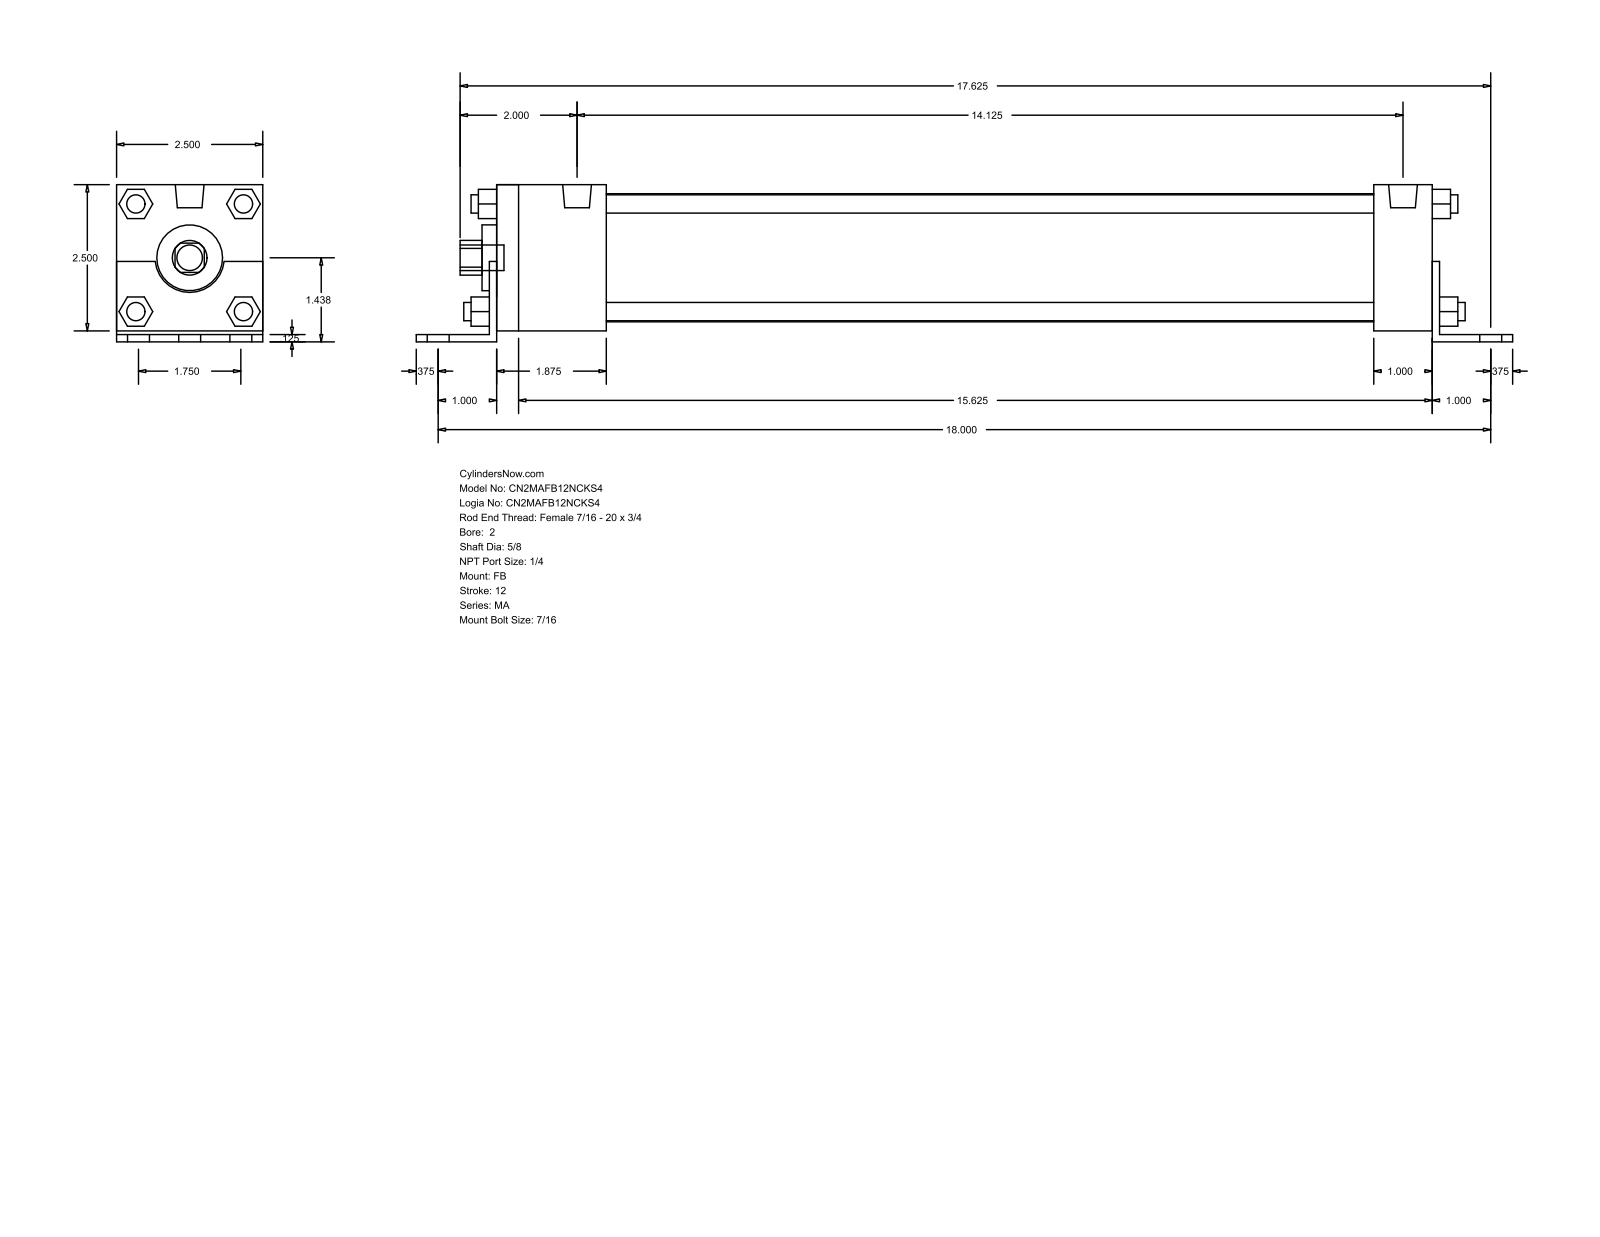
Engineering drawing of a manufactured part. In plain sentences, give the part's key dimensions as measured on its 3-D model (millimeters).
The part is named "MA_FB__0200_0.625". Its 3-D file was written by "GSSL Pune (CONFIG_CONTROL_DESIGN)". It is 0 solids with 140 faces: 105 planar, 35 cylindrical and 0 other. Overall it measures 476.25 by 68.26 by 63.5 millimeters. Round holes: 1 of diameter 15.88, 1 of diameter 28.57, 1 of diameter 55.63. Round bosses or shafts: 8 of diameter 7.94, 7 of diameter 11.11, 2 of diameter 12.49. Partial cylindrical surfaces (rounded edges, fillets, slot ends): 1 of radius 7.54, 1 of radius 15.05. The main face-to-face distances are 63.5, 4.76, 3.17, 68.26, 1.59, 3.18, 65.09, 409.57, 406.39, 12.7.
